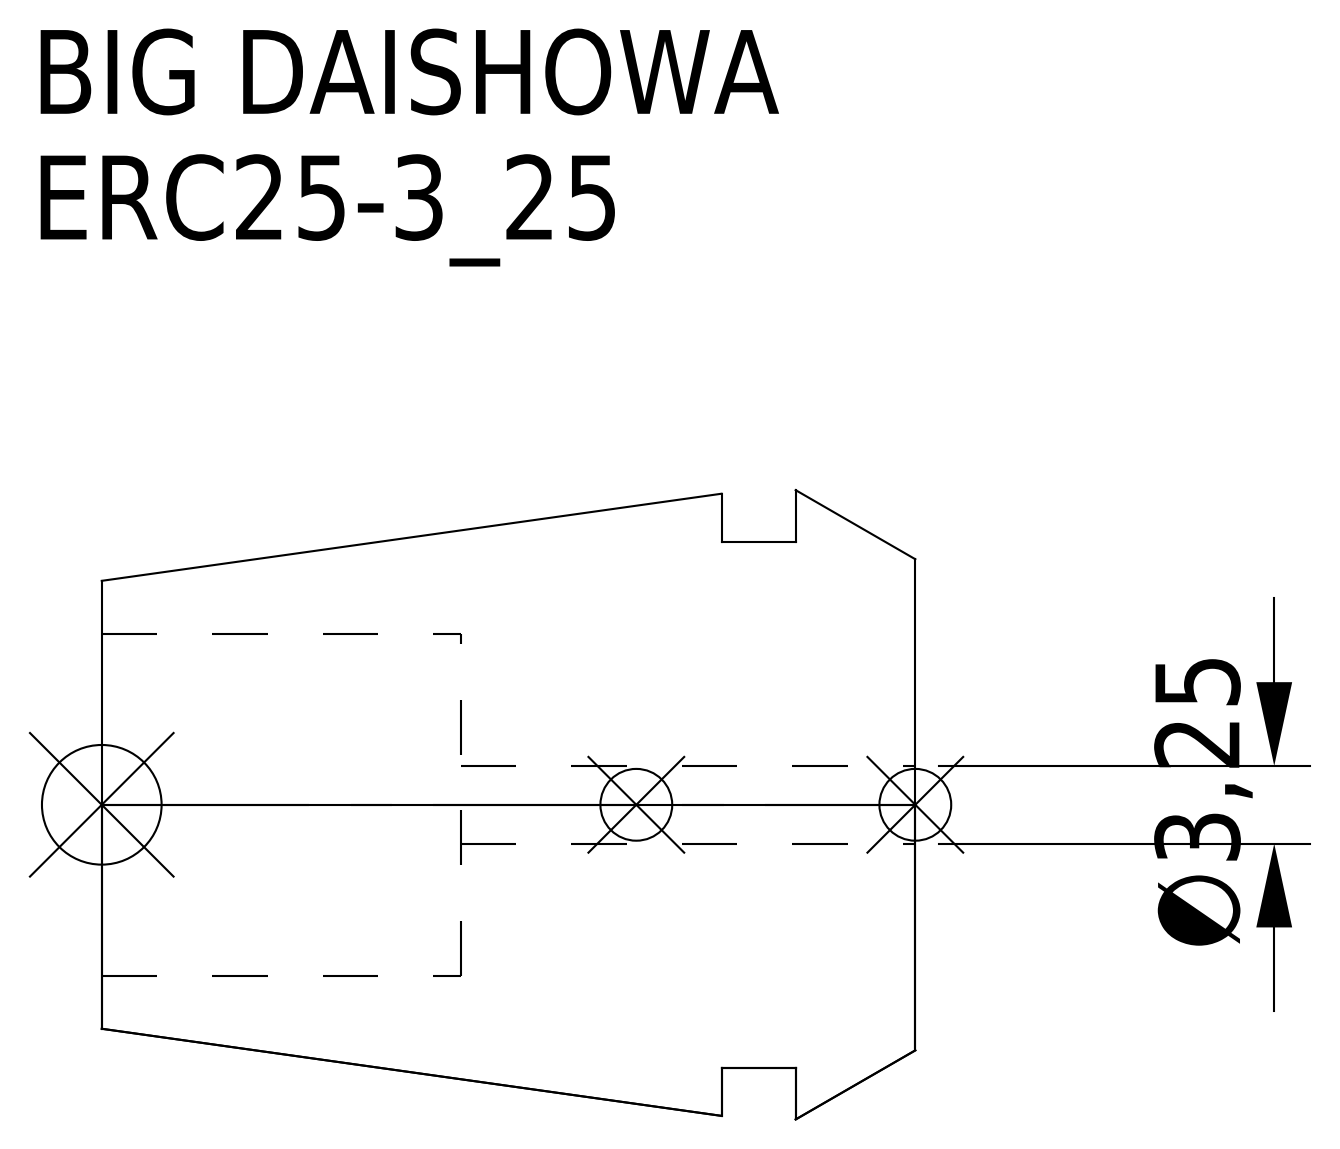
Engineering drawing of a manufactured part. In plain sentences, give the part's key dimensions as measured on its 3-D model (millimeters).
The part is named "ERC25-3_25". Its 3-D file was written by "CREO PARAMETRIC BY PTC INC, 2016380 (AUTOMOTIVE_DESIGN)". It is 1 solid with 15 faces: 5 planar, 6 cylindrical and 4 other. Overall it measures 34 by 26.3 by 26.3 millimeters. Its volume is 11 036 cubic millimeters and its surface area 4 248 square millimeters. Round holes: 1 of diameter 3.25, 1 of diameter 14.3. Round bosses or shafts: 1 of diameter 22. The main face-to-face distances are 5, 19, 14, 8.1, 3.1, 10.9, 34, 29, 25.9, 15.
